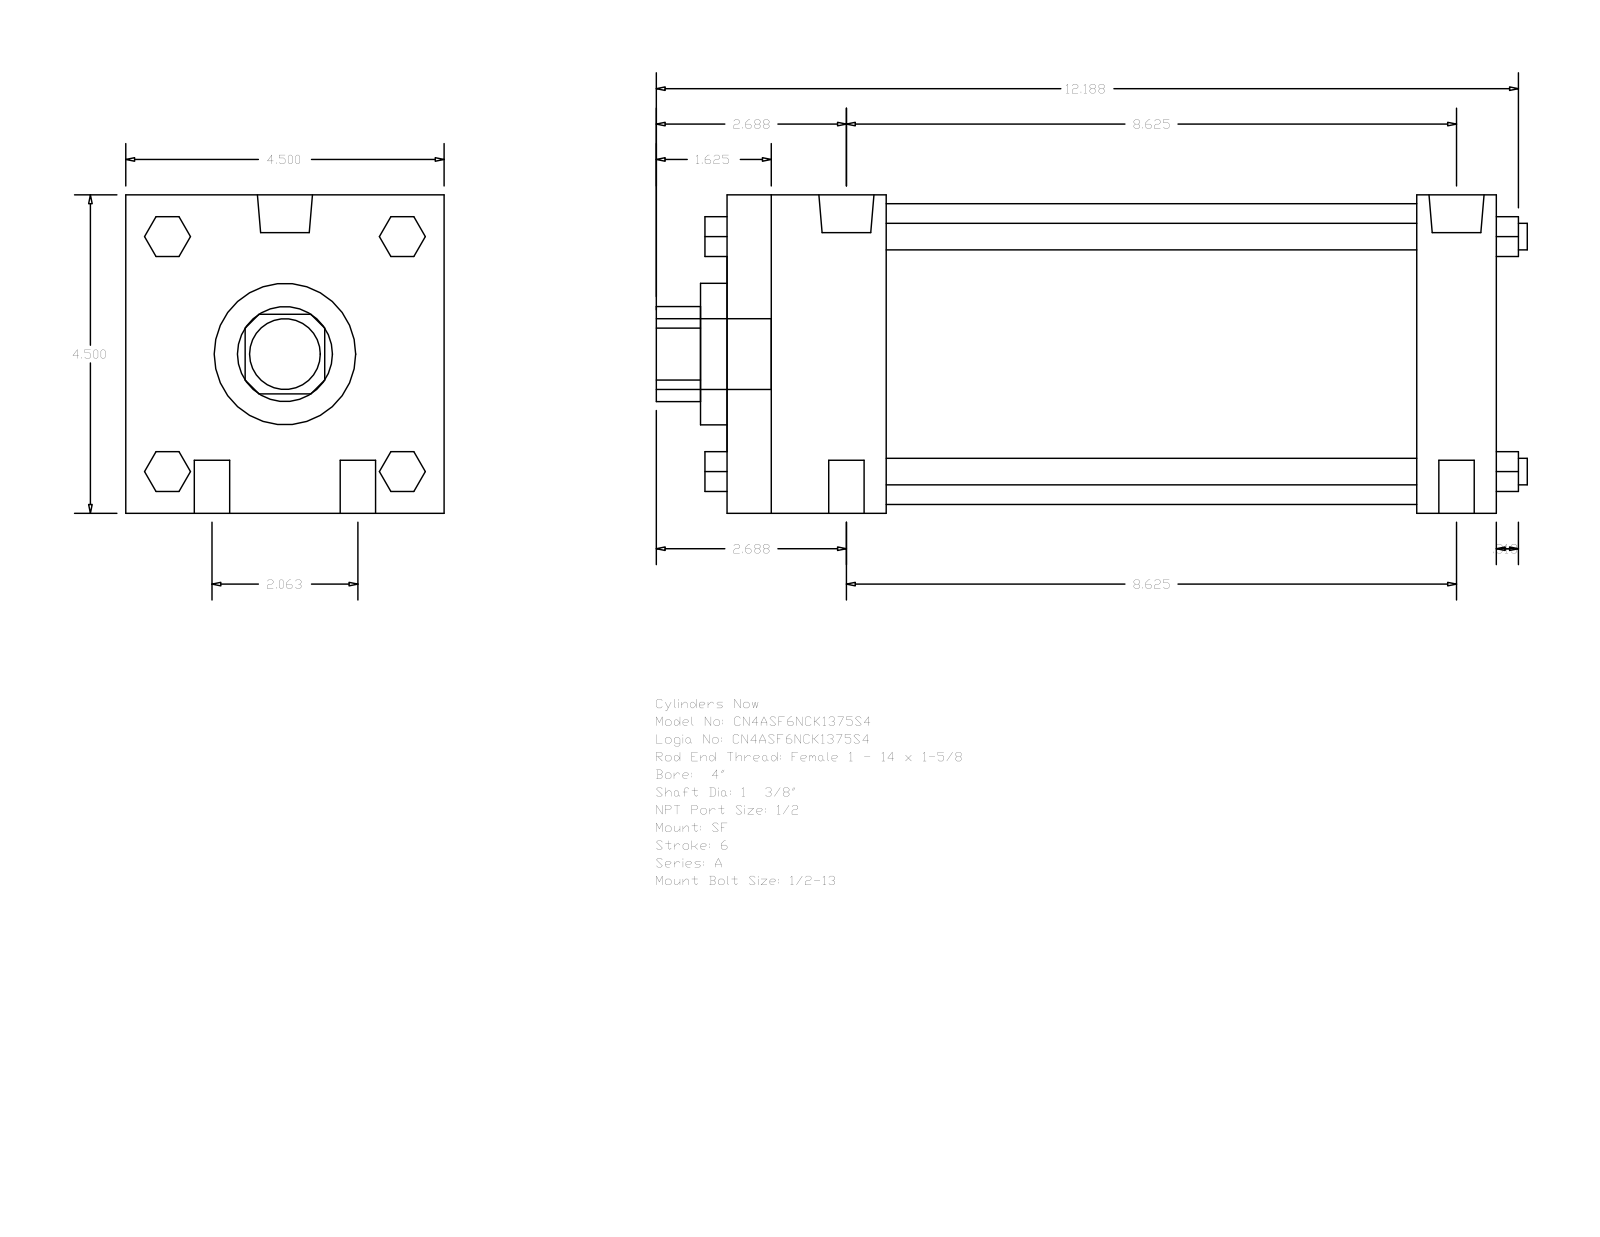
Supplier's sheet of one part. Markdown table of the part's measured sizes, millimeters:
| quantity | value |
| --- | --- |
| part name | A_SF__0400_1.375 |
| STEP written by | GSSL Pune (CONFIG_CONTROL_DESIGN) |
| units | millimeters |
| bodies | 0 solids, 124 faces (94 planar, 30 cylindrical, 0 other) |
| overall size | 312.74 × 114.3 × 114.3 |
| round holes (diameter × count) | 34.92 × 1, 50.8 × 1, 107.95 × 1 |
| round bosses / shafts (diameter × count) | 12.7 × 4, 9.53 × 4, 19.77 × 2, 8.73 × 2, 25.4 × 1 |
| partial cylindrical surfaces (radius × count) | 17.06 × 1 |
| main face-to-face distances | 114.3, 276.22, 28.57, 247.65, 57.15, 190.5, 219.07, 14.29, 9.52, 66.67 |
